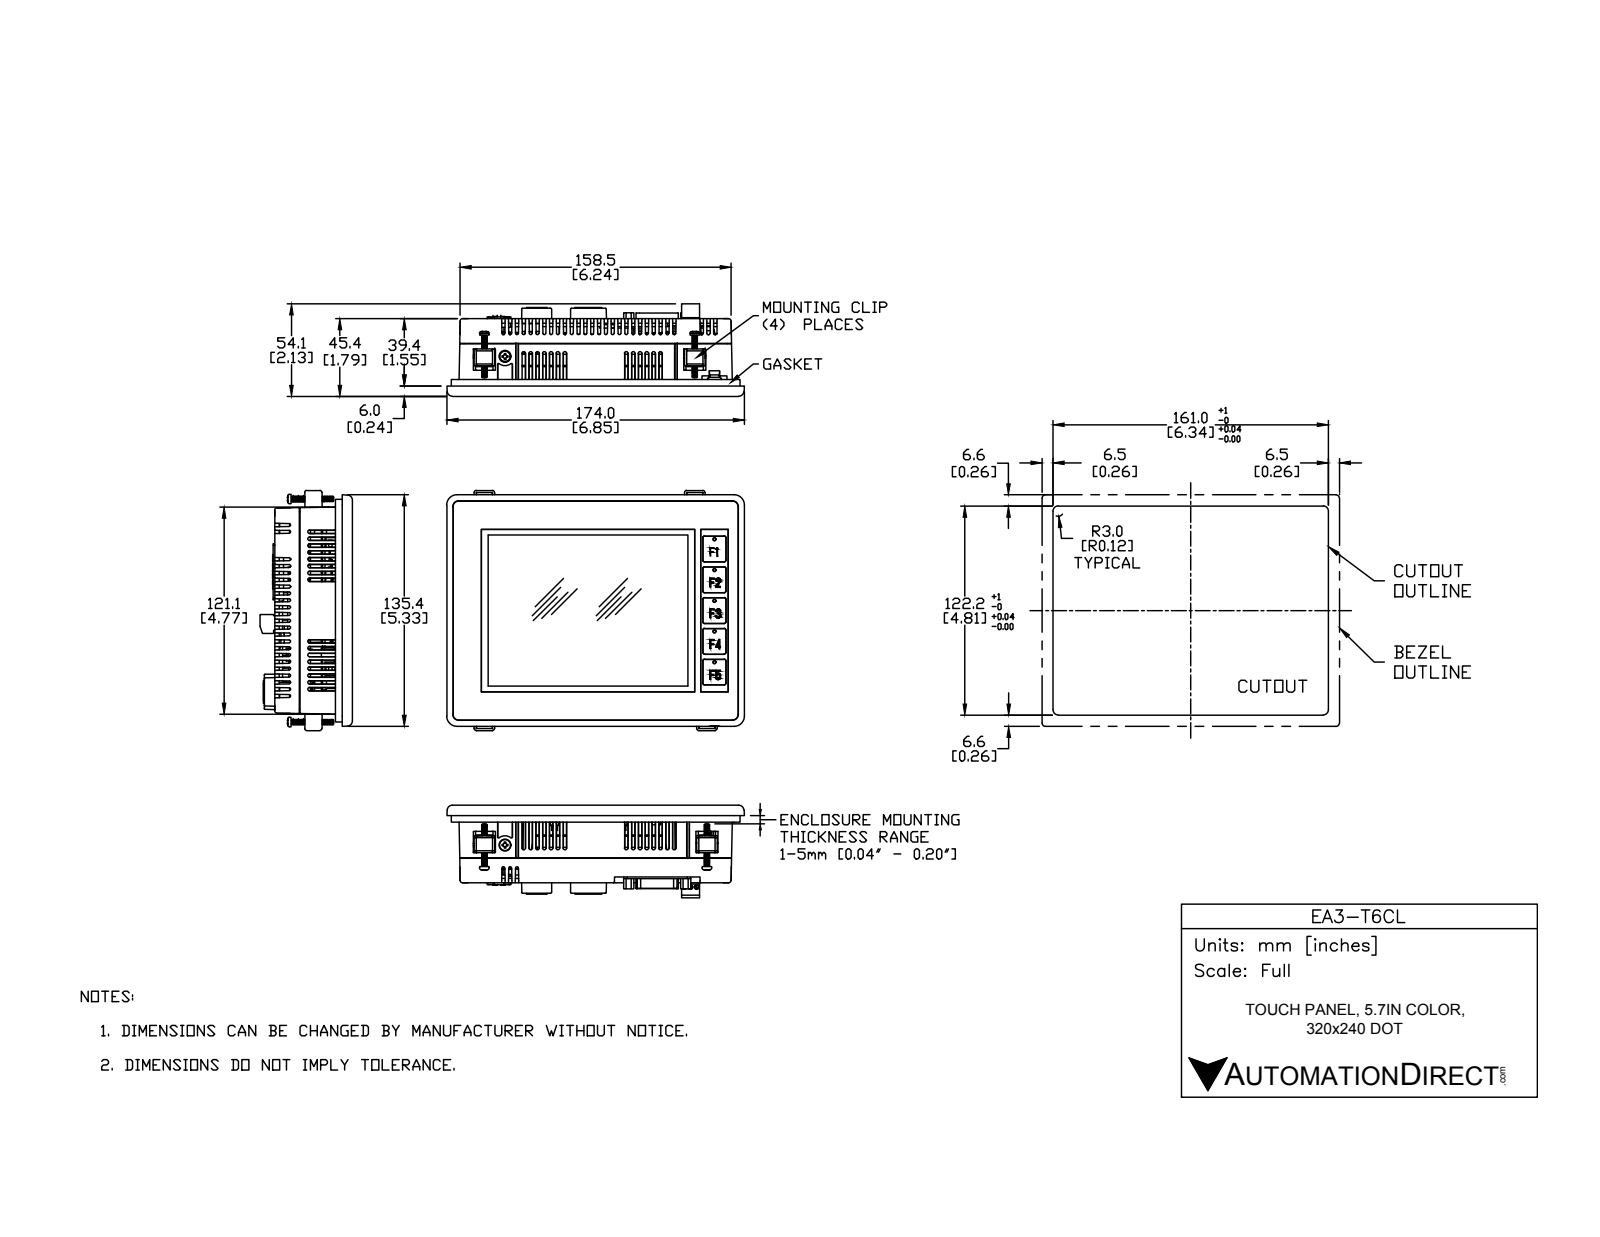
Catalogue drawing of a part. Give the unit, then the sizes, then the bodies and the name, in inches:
Units: inches
Overall size (bounding box): 6.85 × 5.331 × 2.13
Round holes (diameter × count): ⌀0.039 ×18, ⌀0.071 ×5, ⌀0.138 ×5, ⌀0.024 ×4, ⌀0.036 ×4, ⌀0.157 ×4, ⌀0.11 ×3, ⌀0.098 ×2, ⌀0.12 ×2, ⌀0.091 ×1, ⌀0.276 ×1
Round bosses / shafts (diameter × count): ⌀0.043 ×6, ⌀0.248 ×4, ⌀0.118 ×4, ⌀0.031 ×3, ⌀0.12 ×2, ⌀0.217 ×1
Partial cylindrical surfaces — rounded edges, fillets, slot ends (radius × count): R0.039 ×119, R0.034 ×58, R0.012 ×49, R0.02 ×45, R0.031 ×16, R0.098 ×12, R0.079 ×9, R0.008 ×8
Main face-to-face distances: 1.768, 1.78, 0.154, 0.157, 0.217, 0.315, 0.382, 0.37, 1.398, 1.551
Hole centre spacings: 0.124, 0.218, 0.109, 0.198, 0.198, 0.295, 0.327, 0.436
Volume: 53.74 in³ · Surface area: 159.4 in²
Bodies: 1 solid, 4176 faces (3037 planar, 928 cylindrical, 211 other)
Part name (STEP PRODUCT): EA3-T6CL_150625
STEP written by: SolidWorks 2015 (AUTOMOTIVE_DESIGN)
